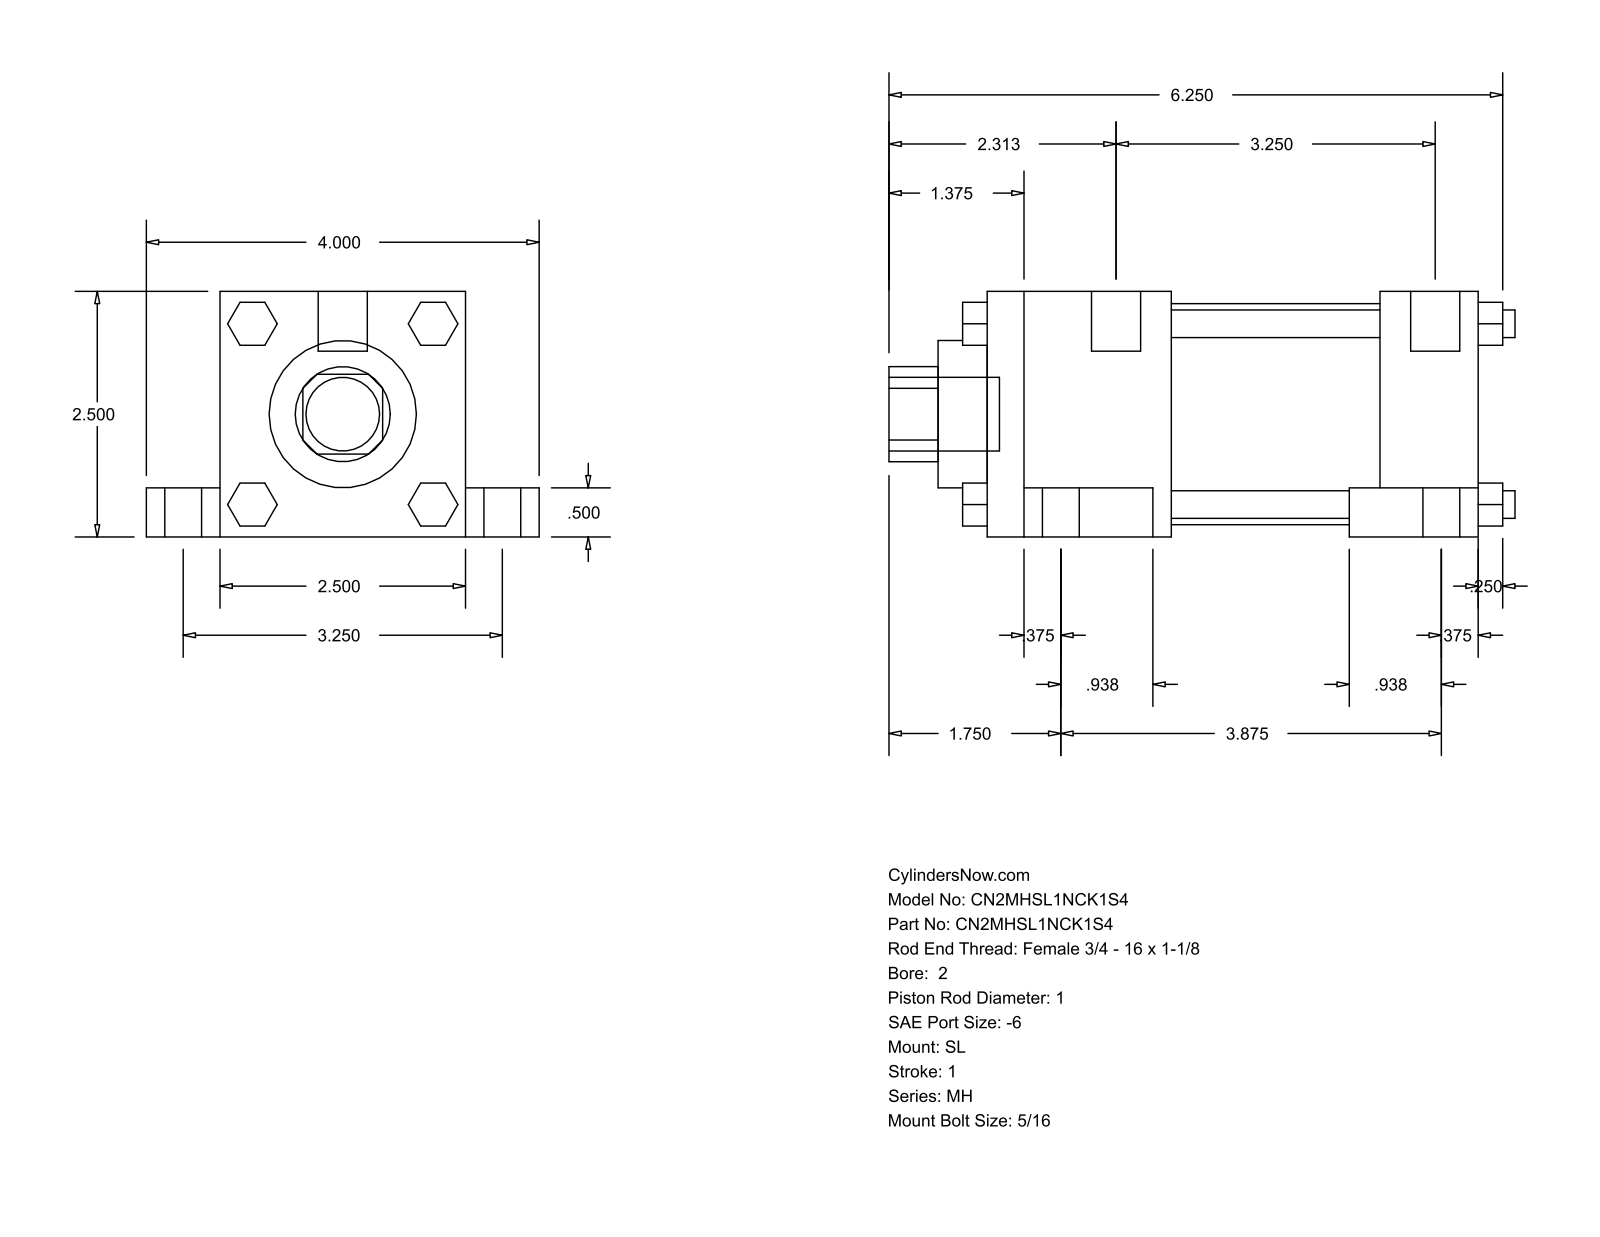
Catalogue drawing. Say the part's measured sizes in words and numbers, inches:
The part is named "MH_SL__0200_1". Its 3-D file was written by "GSSL Pune (CONFIG_CONTROL_DESIGN)". It is 0 solids with 148 faces: 112 planar, 36 cylindrical and 0 other. Overall it measures 6.375 by 4 by 2.5 inches. Round holes: 1 of diameter 1, 1 of diameter 1.5, 1 of diameter 2.25. Round bosses or shafts: 4 of diameter 0.625, 4 of diameter 0.375, 4 of diameter 0.281, 4 of diameter 0.219, 2 of diameter 0.5, 1 of diameter 0.75. Partial cylindrical surfaces (rounded edges, fillets, slot ends): 1 of radius 0.484. The main face-to-face distances are 2.5, 5, 0.5, 2, 4, 0.75, 3.25, 1, 0.375, 1.875.
